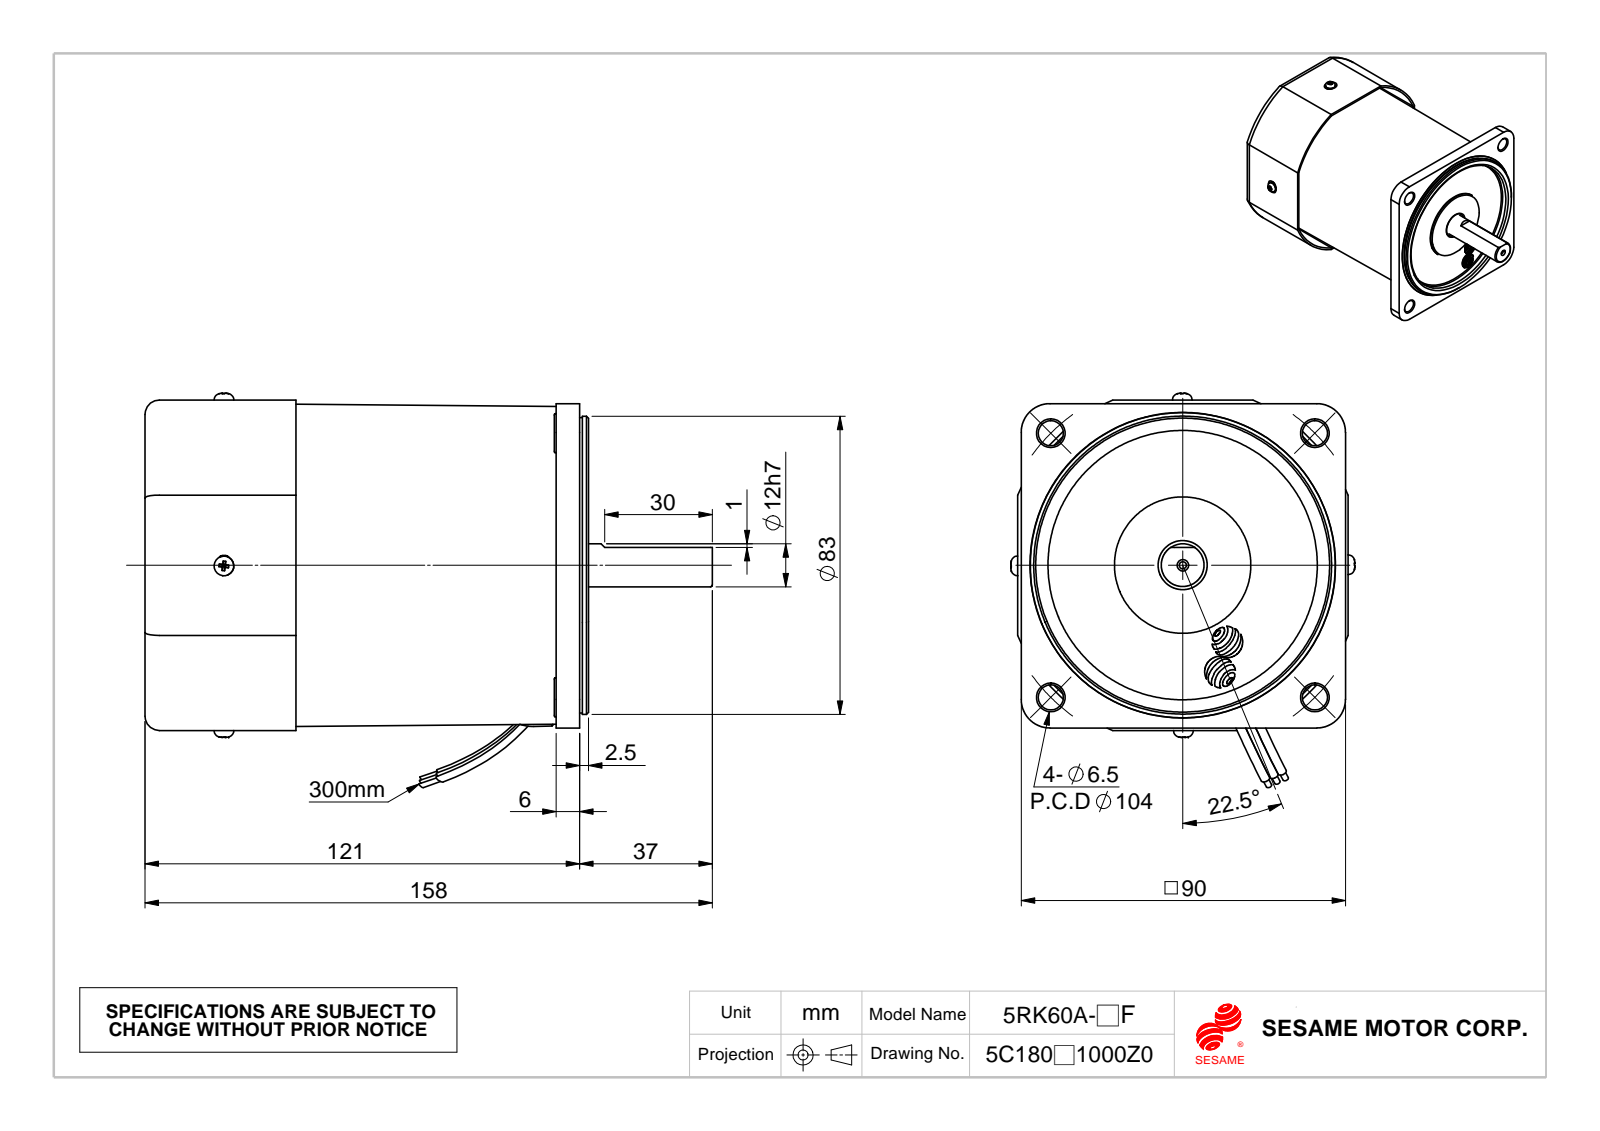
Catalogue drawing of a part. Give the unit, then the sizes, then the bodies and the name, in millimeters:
Units: millimetres
Overall size (bounding box): 158 × 109.84 × 95.83
Round holes (diameter × count): ⌀2.5 ×5, ⌀7 ×4, ⌀2 ×1, ⌀6.5 ×1, ⌀7.2 ×1, ⌀9.5 ×1, ⌀13.7 ×1, ⌀24 ×1, ⌀26 ×1, ⌀40 ×1, ⌀54 ×1, ⌀58.1 ×1
Round bosses / shafts (diameter × count): ⌀5.5 ×4, ⌀3 ×4, ⌀84.22 ×1, ⌀83 ×1, ⌀82.2 ×1, ⌀47 ×1, ⌀38 ×1, ⌀31 ×1
Partial cylindrical surfaces — rounded edges, fillets, slot ends (radius × count): R0.3 ×16, R0.25 ×8, R0.78 ×8, R1 ×8, R1.5 ×8, R1.66 ×8, R2.92 ×8, R0.2 ×4
Main face-to-face distances: 1, 118.5, 91, 16, 102.5, 118.4, 119.4, 0.9, 117.5, 119.5
Hole centre spacings: 52, 73.54, 104
Volume: 685 613 mm³ · Surface area: 102 068 mm²
Bodies: 12 solids, 657 faces (199 planar, 322 cylindrical, 136 other)
Part name (STEP PRODUCT): 風扇蓋FC-9042-21; M560; 60A; 線扣
STEP written by: SolidWorks 2010 (CONFIG_CONTROL_DESIGN)
